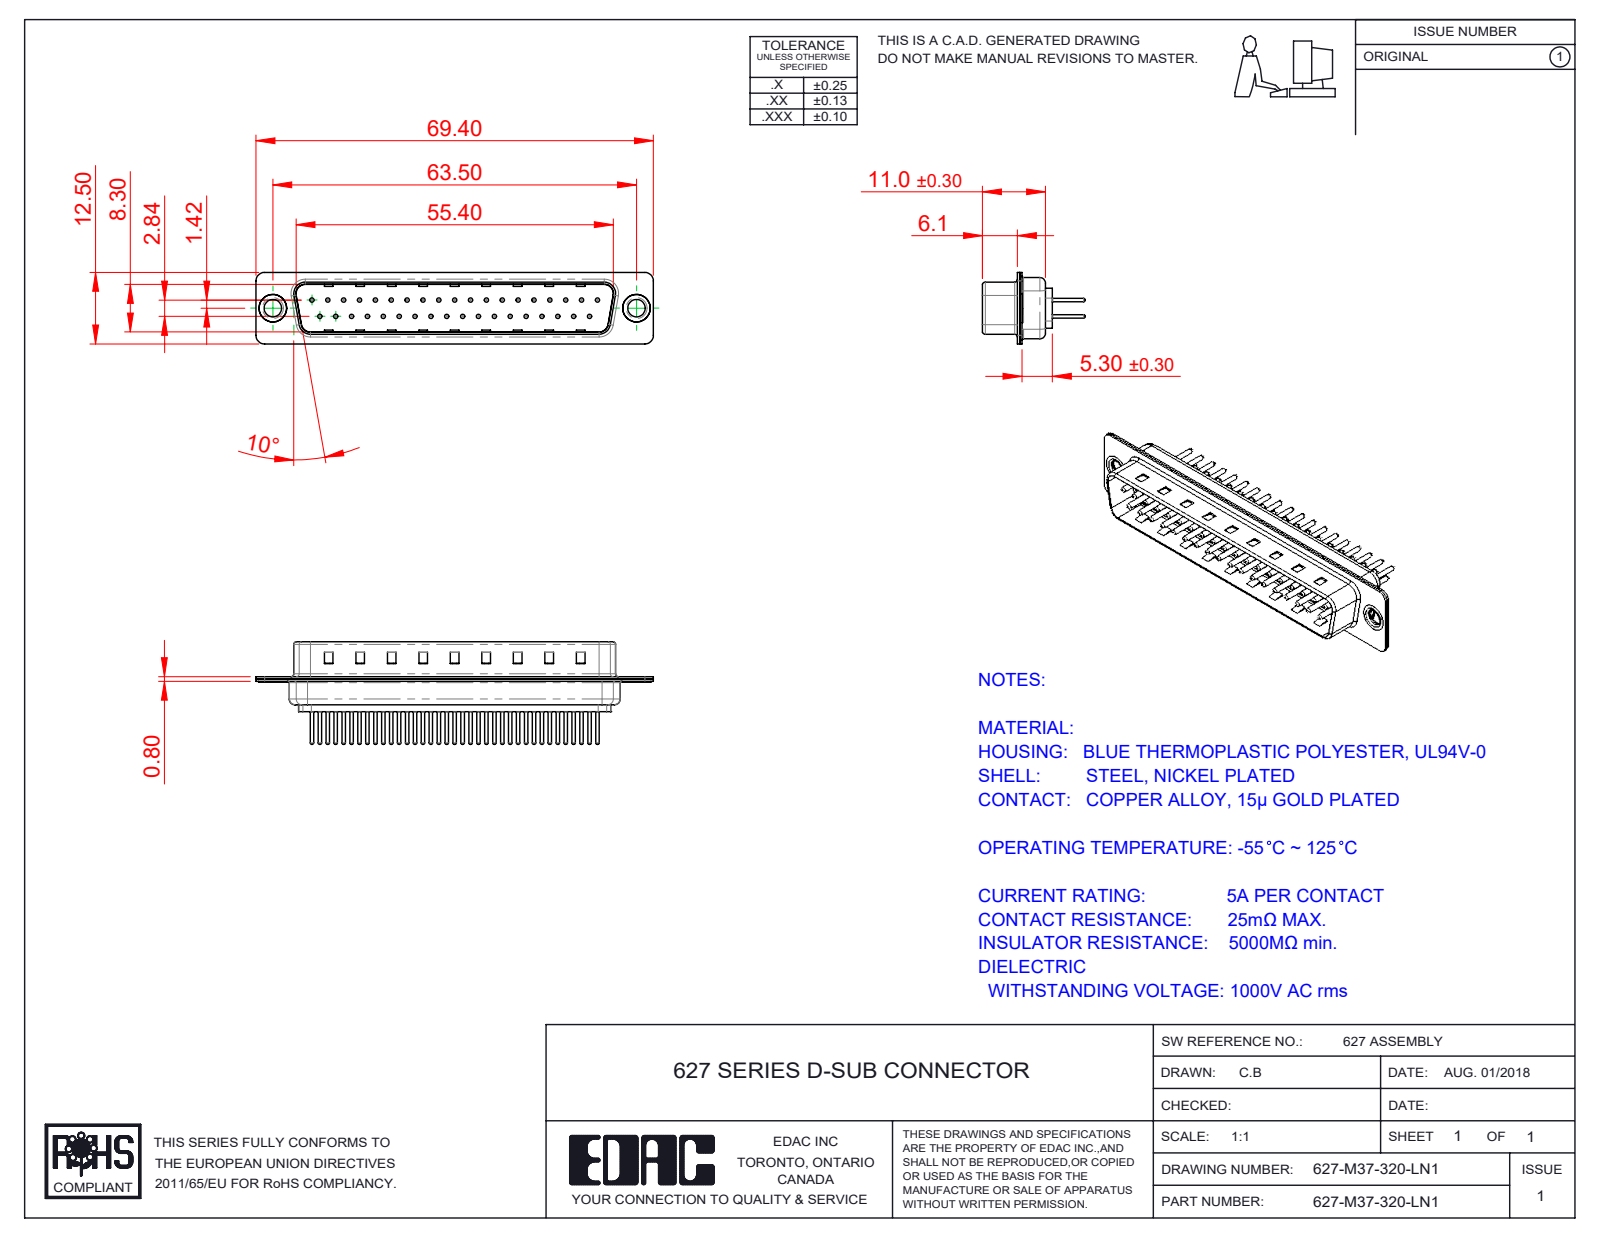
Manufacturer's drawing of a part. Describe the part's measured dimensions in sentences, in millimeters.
The part is named "627M Contact Row 1_20; 627M Shell Rear_37 Contacts; 627M Thru Hole Rivet; 627M Housing_37 Contacts (+3 more)". Its 3-D file was written by "SolidWorks 2020 (CONFIG_CONTROL_DESIGN)". It is 42 solids with 1755 faces: 462 planar, 643 cylindrical and 650 other. Overall it measures 69.4 by 17.9 by 12.5 millimeters. Its volume is 3 690 cubic millimeters and its surface area 9 124 square millimeters. Round holes: 37 of diameter 0.75, 37 of diameter 1.6, 37 of diameter 2, 2 of diameter 3.05, 2 of diameter 4, 2 of diameter 4.8. Round bosses or shafts: 37 of diameter 1.5, 37 of diameter 0.6, 2 of diameter 5, 2 of diameter 4.9, 2 of diameter 3.55. Partial cylindrical surfaces (rounded edges, fillets, slot ends): 16 of radius 1.5, 12 of radius 2, 8 of radius 0.5, 8 of radius 1.6, 4 of radius 0.25, 4 of radius 0.6, 4 of radius 0.65, 4 of radius 0.9. The main face-to-face distances are 0.4, 0.8, 9.5, 9.1, 8.7, 9.9, 1.2, 5.7, 0.75, 0.35. The hole center spacings are 2.77, 5.54, 3.16, 8.31, 11.08, 13.85, 16.62, 19.39.
